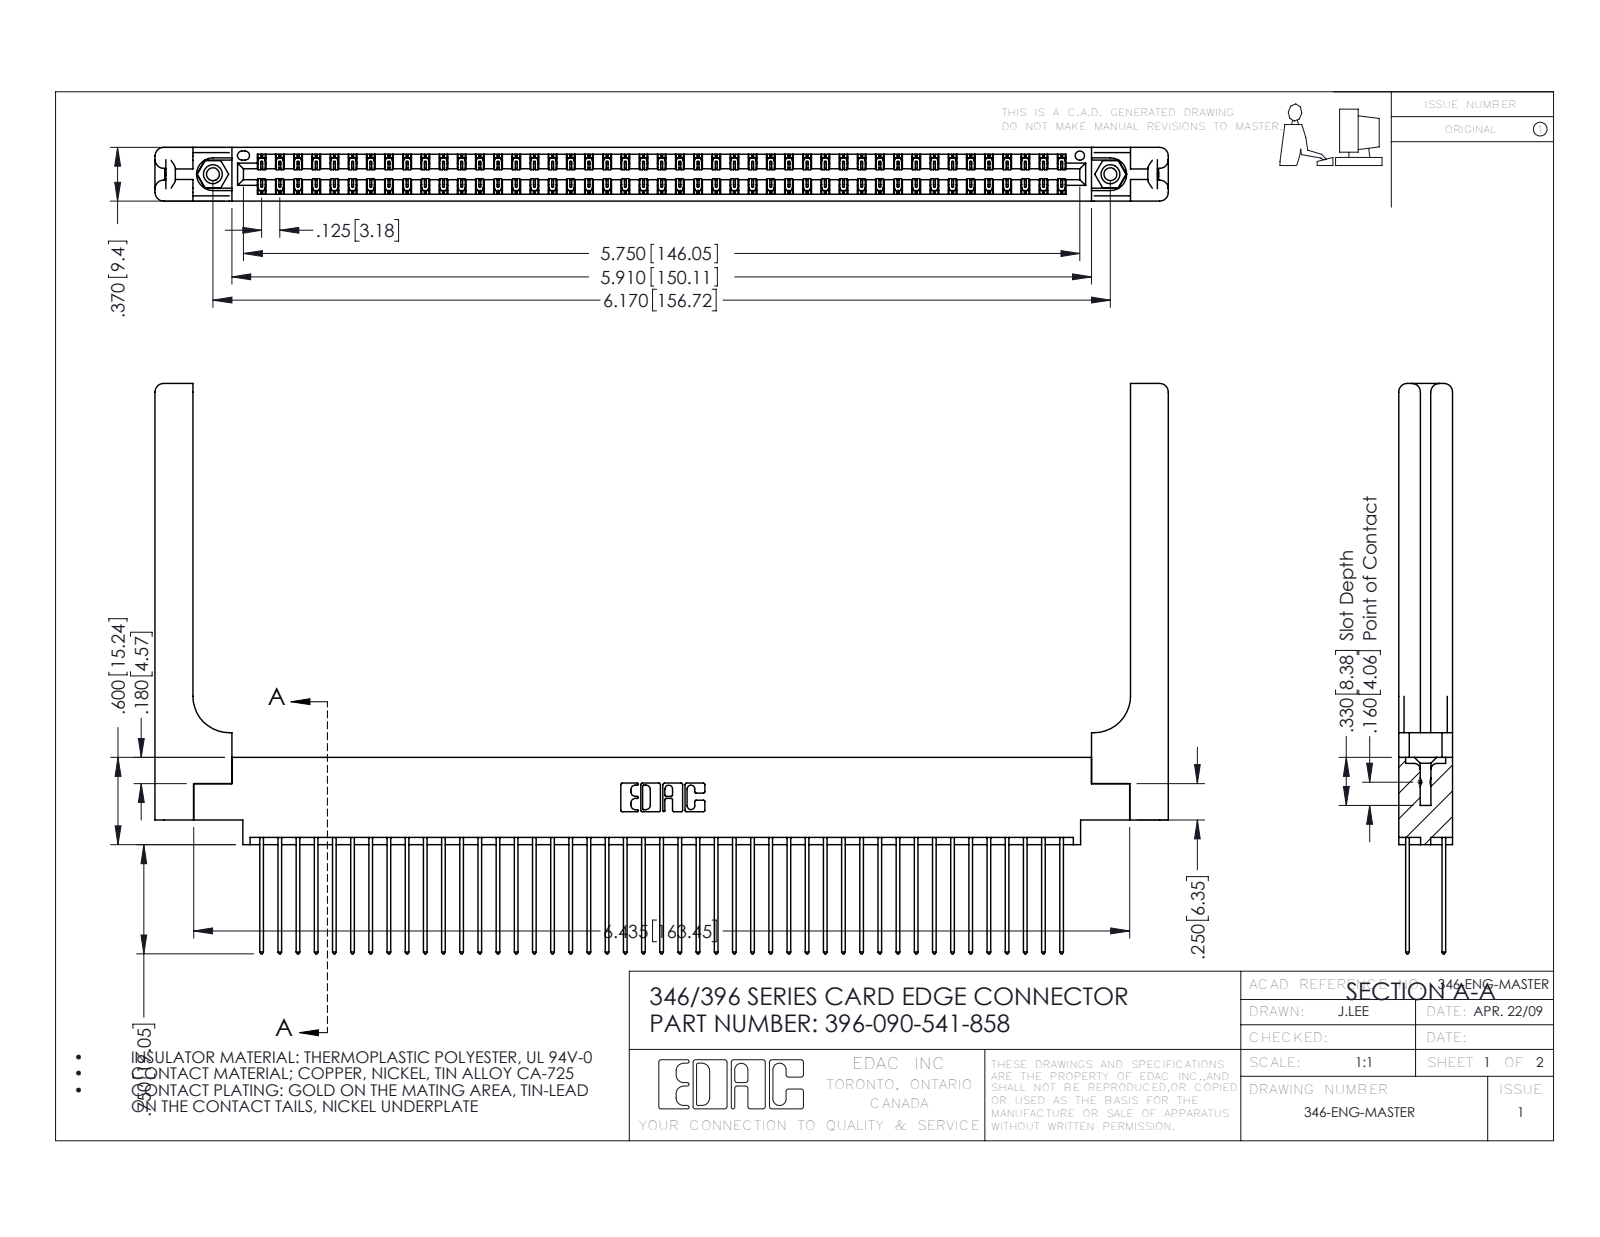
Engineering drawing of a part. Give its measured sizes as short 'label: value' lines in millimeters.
name: 346-220-058_345-220-058; 345-292-001_345-293-141; 396-090-541-858; 346 Part_0.170 Offset - 0.156 Dia-TH (+1 more)
written by: SolidWorks 2016 (CONFIG_CONTROL_DESIGN)
unit: mm
bodies: 95 solids, 5062 faces (3378 planar, 1624 cylindrical, 60 other)
size: 176.9 × 99.6 × 9.4
volume: 25 140 mm³; area: 31 920 mm²
holes: 2× ⌀2.3, 2× ⌀3.2, 2× ⌀4, 1× ⌀1.6
bosses: 2× ⌀3.9
rounds: 135× R0.2, 90× R0.3, 22× R0.3, 16× R1.5, 6× R0.2, 6× R0.8, 3× R0.7, 2× R0.4
face distances: 1.2, 8.2, 1.8, 9.4, 6.4, 0.6, 7.6, 7, 3.8, 3.8
hole spacings: 6.2, 151.4, 156.7
